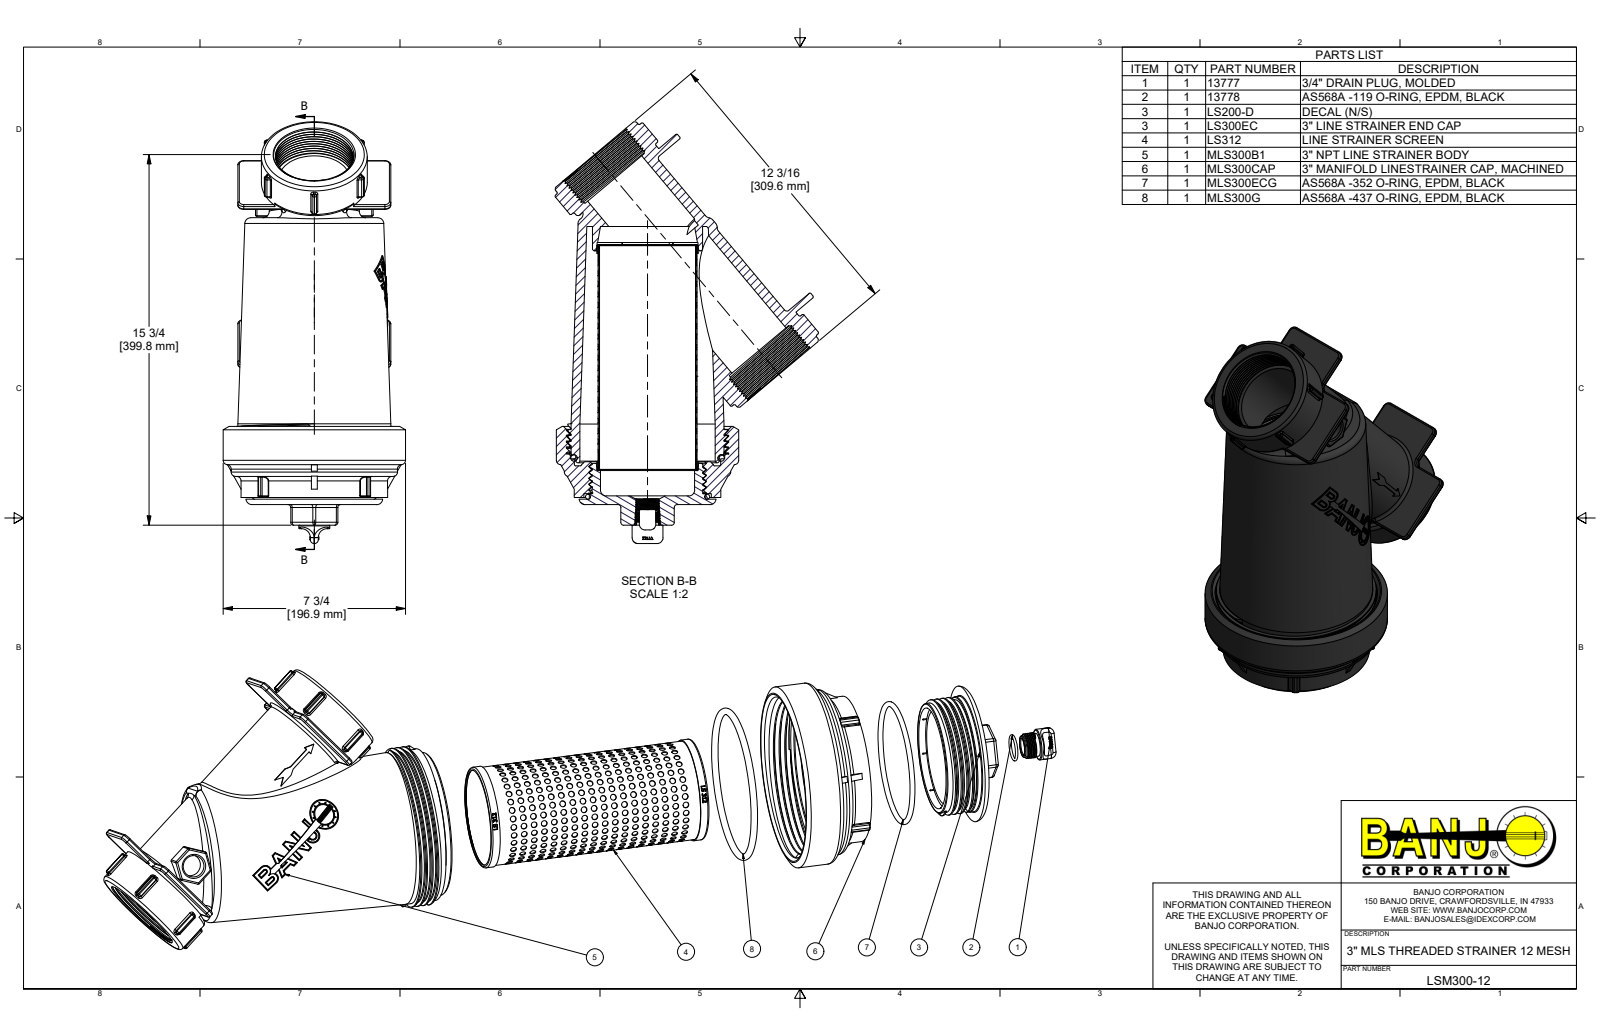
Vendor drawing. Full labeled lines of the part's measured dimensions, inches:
Part name (STEP PRODUCT): LSM300-12; MLS300B1; 13777; 13778 (+7 more)
STEP written by: Autodesk Inventor 2022 (AUTOMOTIVE_DESIGN)
Units: inches
Bodies: 11 solids, 2230 faces (594 planar, 1072 cylindrical, 564 other)
Overall size (bounding box): 17.915 × 11.198 × 7.75
Volume: 196.4 in³ · Surface area: 1 531 in²
Round holes (diameter × count): ⌀0.25 ×540, ⌀3.3 ×2, ⌀0.7 ×1, ⌀0.817 ×1, ⌀0.91 ×1, ⌀1.154 ×1, ⌀3 ×1, ⌀4 ×1, ⌀4.063 ×1, ⌀4.08 ×1, ⌀4.132 ×1, ⌀4.232 ×1
Round bosses / shafts (diameter × count): ⌀4.5 ×2, ⌀7.75 ×1, ⌀7.07 ×1, ⌀6.8 ×1, ⌀6.5 ×1, ⌀6.23 ×1, ⌀6.1 ×1, ⌀4.955 ×1
Partial cylindrical surfaces — rounded edges, fillets, slot ends (radius × count): R0.06 ×129, R0.09 ×32, R0.03 ×24, R0.25 ×19, R0.125 ×18, R0.02 ×8, R0.015 ×6, R0.071 ×2
Main face-to-face distances: 8.564, 0.3, 0.251, 8.815, 0.23, 10.627, 1.562, 0.37, 0.07, 11.809
Hole centre spacings: 0.446, 0.893, 1.339, 1.786, 2.232, 2.679, 3.125, 3.572
